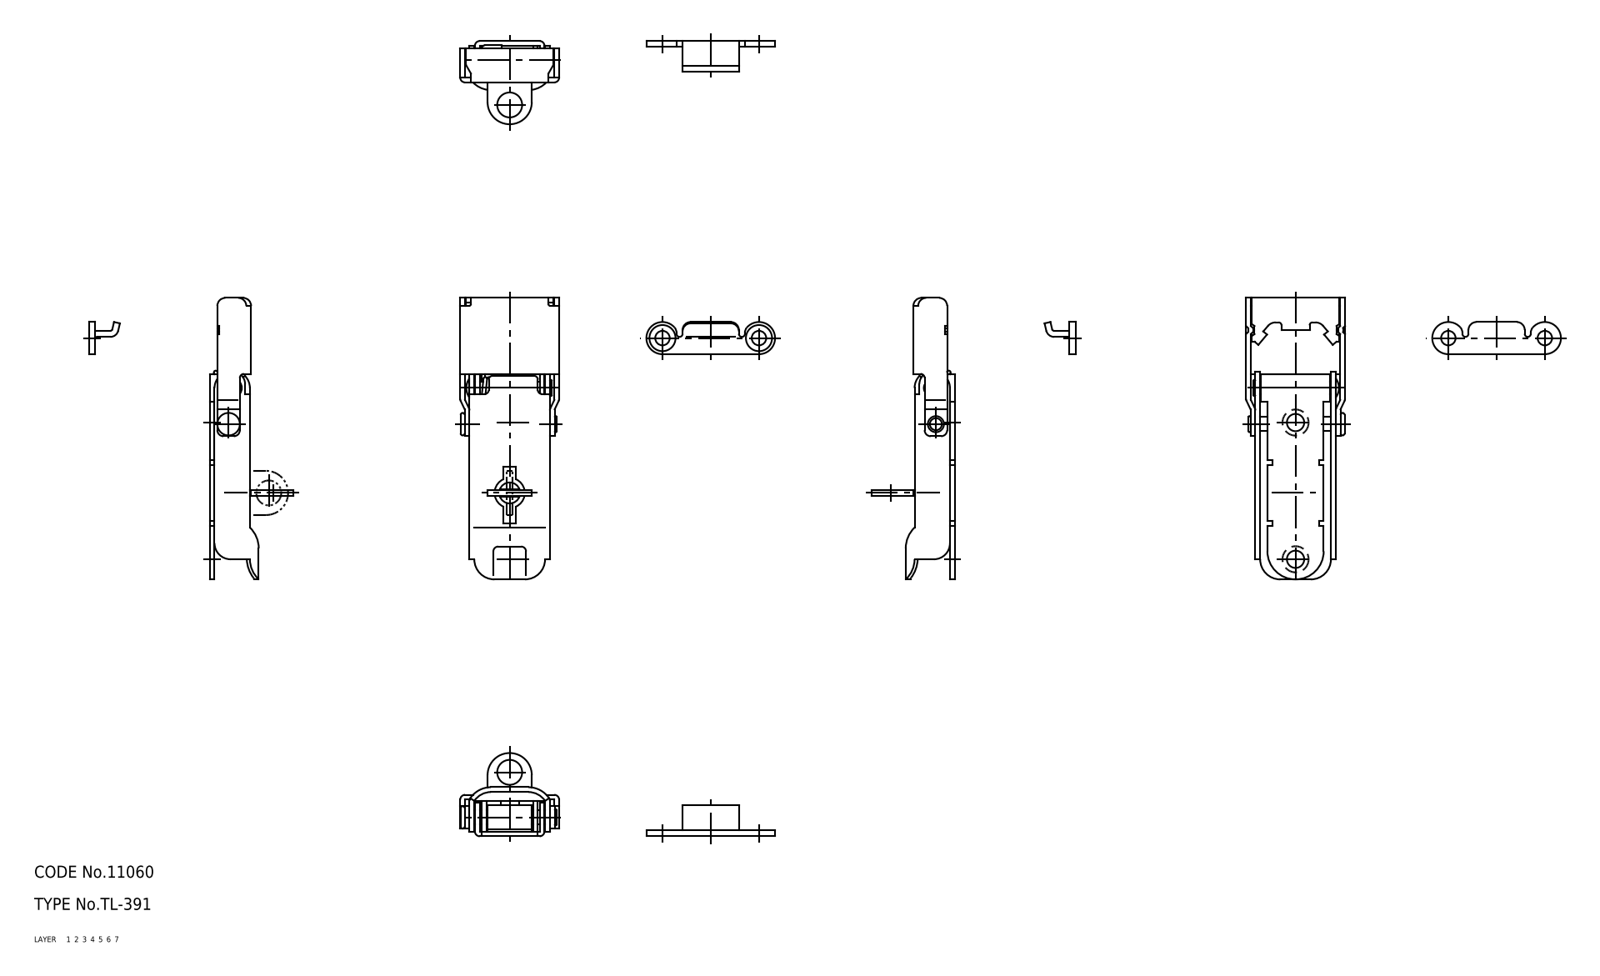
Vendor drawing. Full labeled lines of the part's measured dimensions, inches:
Part name (STEP PRODUCT): 67129478; 67129491; 67129504; 67129517 (+1 more)
STEP written by: CADfix (AUTOMOTIVE_DESIGN)
Units: inches
Bodies: 5 solids, 348 faces (0 planar, 0 cylindrical, 348 other)
Overall size (bounding box): 2.756 × 1.26 × 0.815
Volume: 0.34 in³ · Surface area: 16.6 in²
